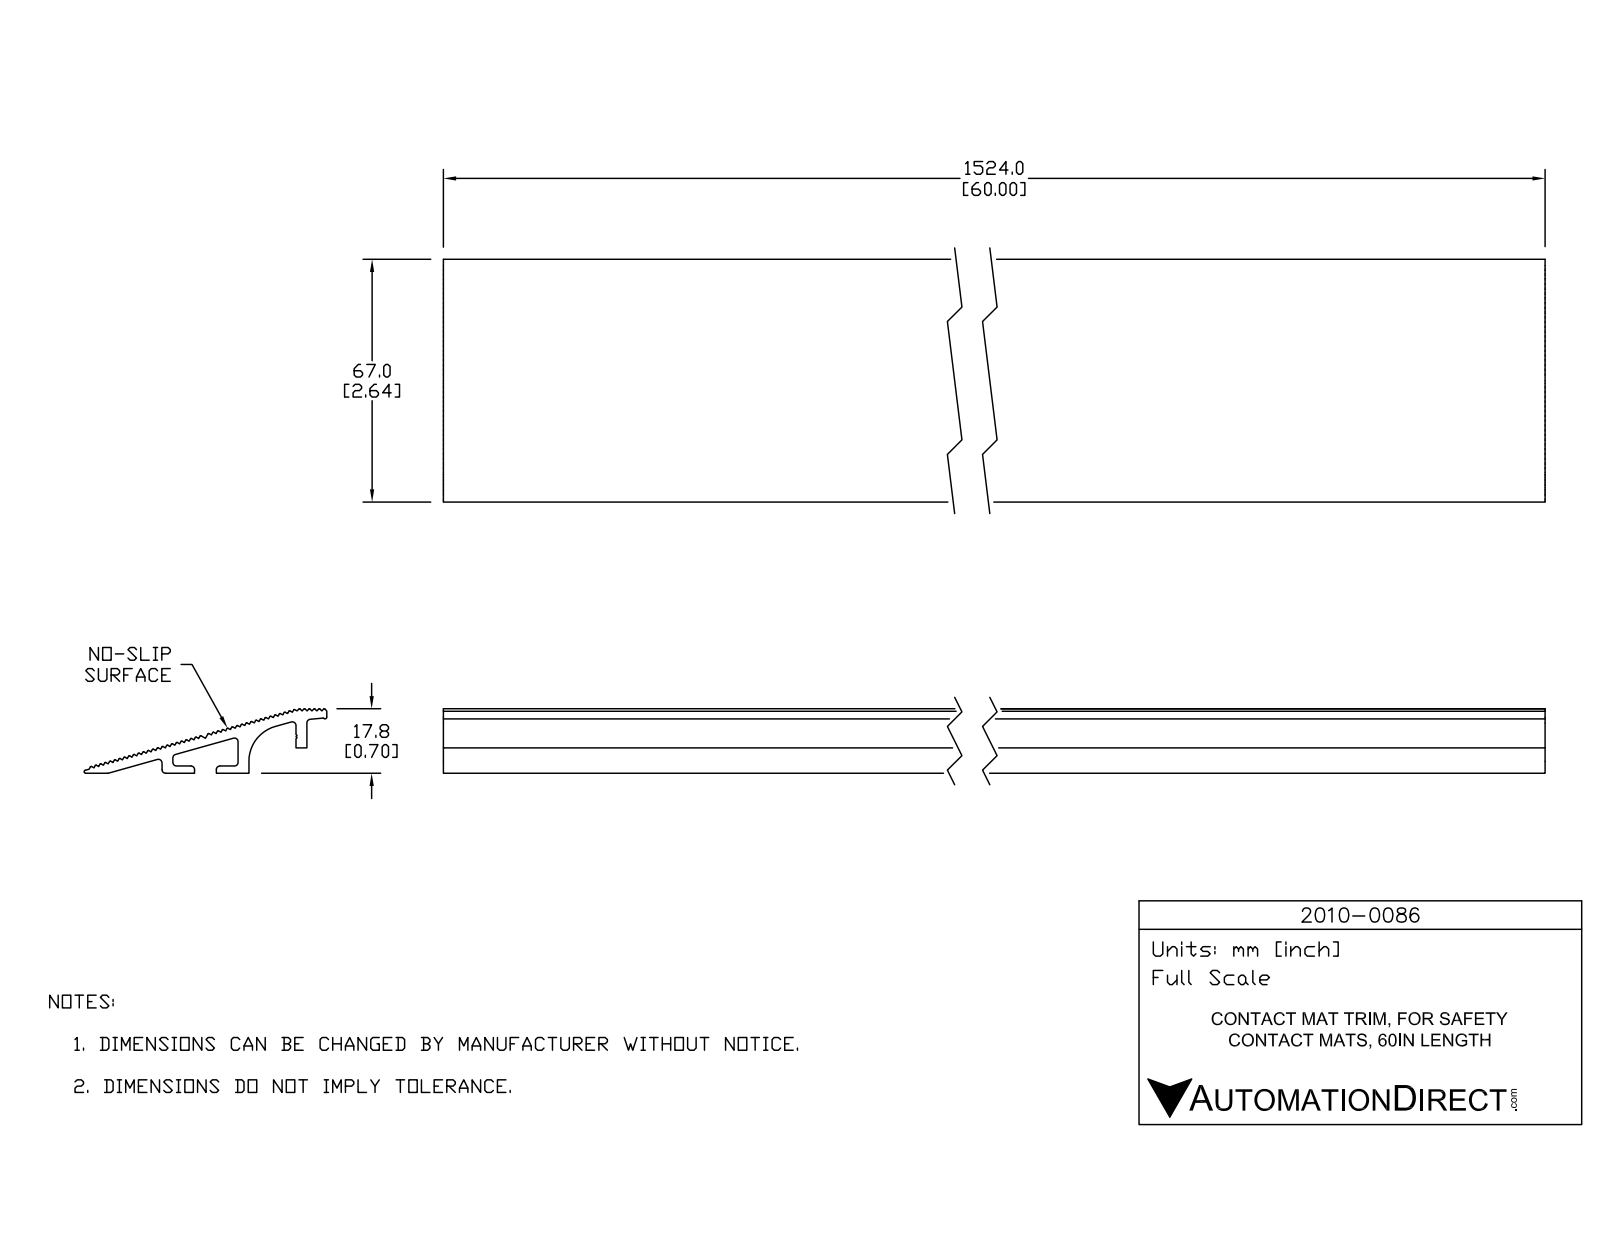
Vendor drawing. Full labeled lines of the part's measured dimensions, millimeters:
Part name (STEP PRODUCT): 2010-0086
STEP written by: SolidWorks 2017 (AUTOMOTIVE_DESIGN)
Units: millimetres
Bodies: 1 solid, 190 faces (125 planar, 65 cylindrical, 0 other)
Overall size (bounding box): 1524 × 67 × 17.8
Volume: 444 313 mm³ · Surface area: 346 663 mm²
Partial cylindrical surfaces — rounded edges, fillets, slot ends (radius × count): R0.2 ×50, R1 ×11, R0.42 ×1, R0.5 ×1, R10 ×1
Main face-to-face distances: 2.9, 1.93, 0.97, 4.83, 3, 16, 2, 7.73, 19, 0.96
